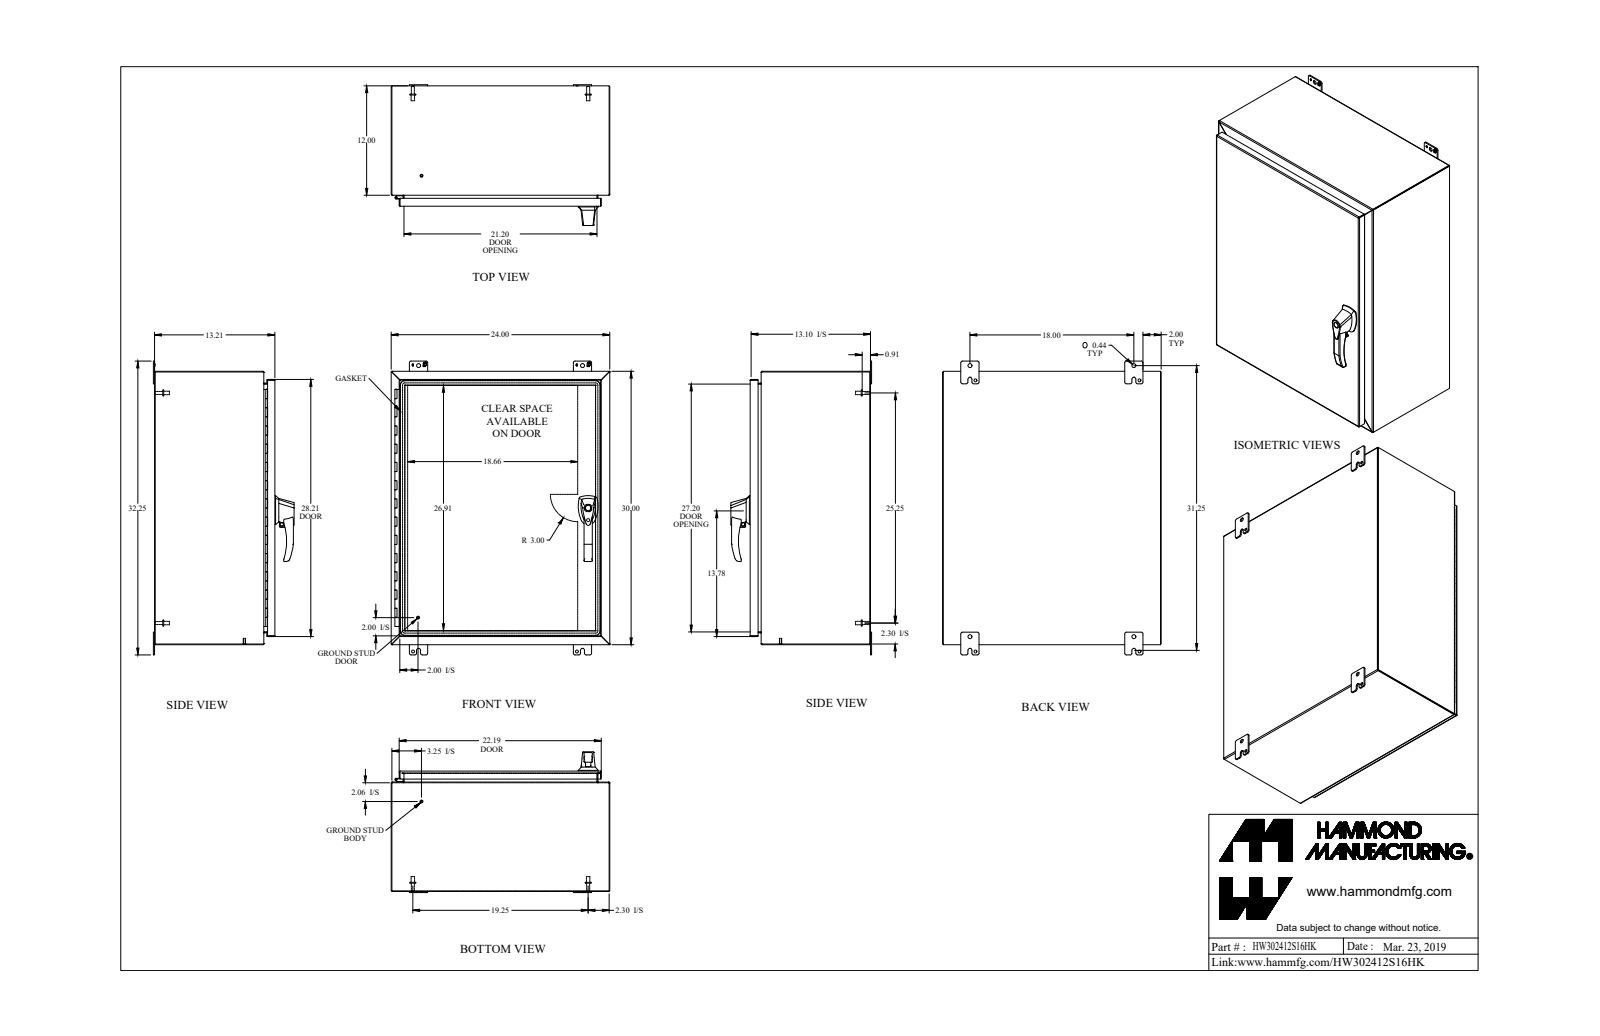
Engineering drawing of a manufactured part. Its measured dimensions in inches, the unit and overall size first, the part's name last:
Units: inches
Overall size (bounding box): 32.25 × 24 × 15.45
Round holes (diameter × count): ⌀0.176 ×6, ⌀0.313 ×5, ⌀0.25 ×3, ⌀0.265 ×3, ⌀0.413 ×3, ⌀0.196 ×2, ⌀0.256 ×2, ⌀0.394 ×2, ⌀0.437 ×2, ⌀0.11 ×1, ⌀0.233 ×1, ⌀0.33 ×1
Round bosses / shafts (diameter × count): ⌀0.375 ×9, ⌀0.25 ×7, ⌀0.156 ×6, ⌀0.65 ×4, ⌀0.332 ×4, ⌀0.313 ×4, ⌀1 ×3, ⌀0.51 ×3
Partial cylindrical surfaces — rounded edges, fillets, slot ends (radius × count): R0.25 ×27, R0.188 ×24, R0.036 ×18, R0.108 ×18, R0.06 ×12, R0.125 ×9, R0.045 ×8, R0.218 ×8
Main face-to-face distances: 0.072, 23.928, 0.072, 13.138, 13.066, 13.138, 13.21, 29.928, 23.856, 24
Hole centre spacings: 1.11, 11.118, 11.119, 22.237, 1.338, 9.78, 10.563, 10.565
Volume: 250.3 in³ · Surface area: 6 547 in²
Bodies: 44 solids, 1420 faces (675 planar, 601 cylindrical, 144 other)
Part name (STEP PRODUCT): HW302412S16HK
STEP written by: SolidWorks 2018 (AUTOMOTIVE_DESIGN)
